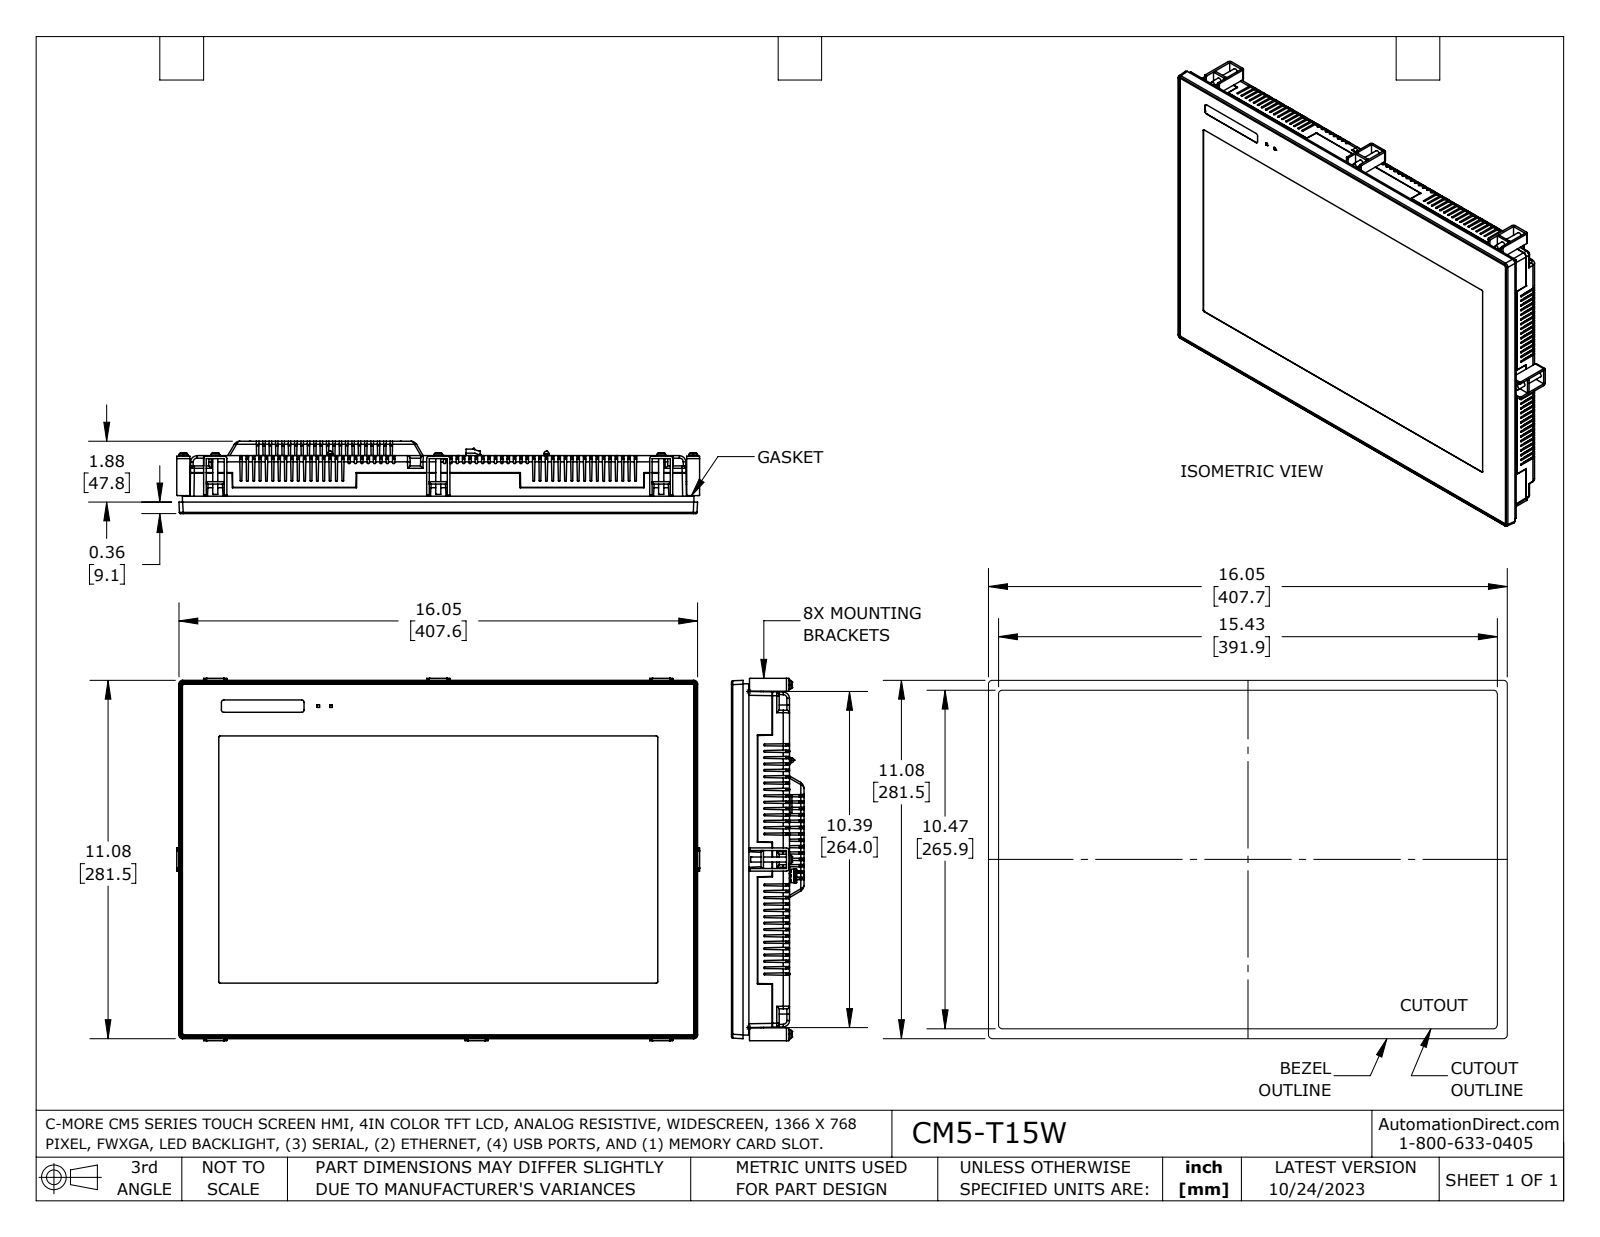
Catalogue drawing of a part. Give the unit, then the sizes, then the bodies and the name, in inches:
Units: inches
Overall size (bounding box): 16.173 × 11.209 × 2.241
Round holes (diameter × count): ⌀0.036 ×15, ⌀0.317 ×6, ⌀0.11 ×4, ⌀0.114 ×3, ⌀0.1 ×2
Round bosses / shafts (diameter × count): ⌀0.276 ×8, ⌀0.157 ×8, ⌀0.138 ×7, ⌀0.018 ×6, ⌀0.102 ×4, ⌀0.11 ×3, ⌀0.217 ×2, ⌀0.164 ×2
Partial cylindrical surfaces — rounded edges, fillets, slot ends (radius × count): R0.02 ×101, R0.039 ×89, R0.012 ×86, R0.008 ×70, R0.079 ×60, R0.01 ×41, R0.038 ×24, R0.024 ×22
Main face-to-face distances: 1.781, 1.791, 0.45, 2.231, 2.241, 0.638, 0.535, 0.094, 1.34, 0.89
Hole centre spacings: 0.124, 0.109, 0.218, 0.327, 0.436, 0.198, 0.198, 0.138
Volume: 281.8 in³ · Surface area: 562.7 in²
Bodies: 4 solids, 4552 faces (2982 planar, 1200 cylindrical, 370 other)
Part name (STEP PRODUCT): CM5-T15W_REV4
STEP written by: SolidWorks 2021 (AUTOMOTIVE_DESIGN)
